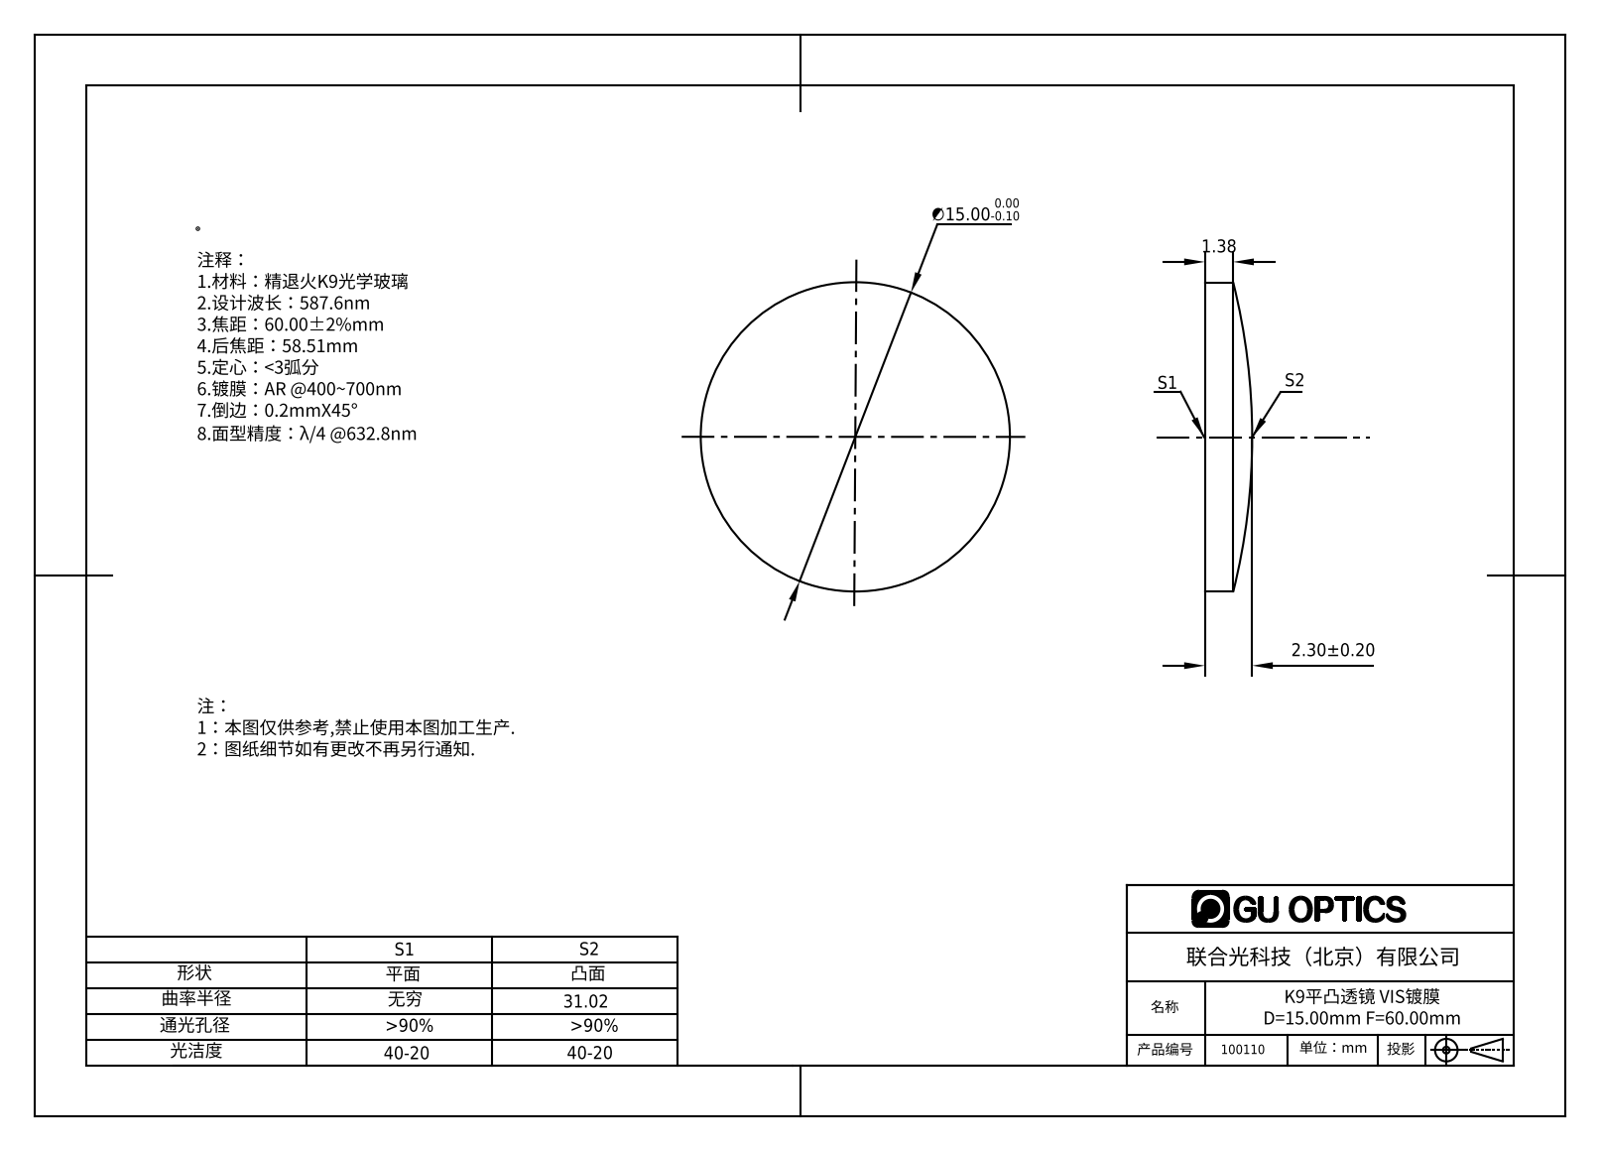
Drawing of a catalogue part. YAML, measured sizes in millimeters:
part_name: "100110"
step_written_by: "SolidWorks 2016 (AUTOMOTIVE_DESIGN)"
units: millimeters
bodies: {solids: 1, faces: 5, planar: 1, cylindrical: 2, other: 2}
overall_size: [15, 15, 2.3]
volume: 326
surface_area: 421
round_bosses_or_shafts:
  - {diameter: 15, count: 1}
